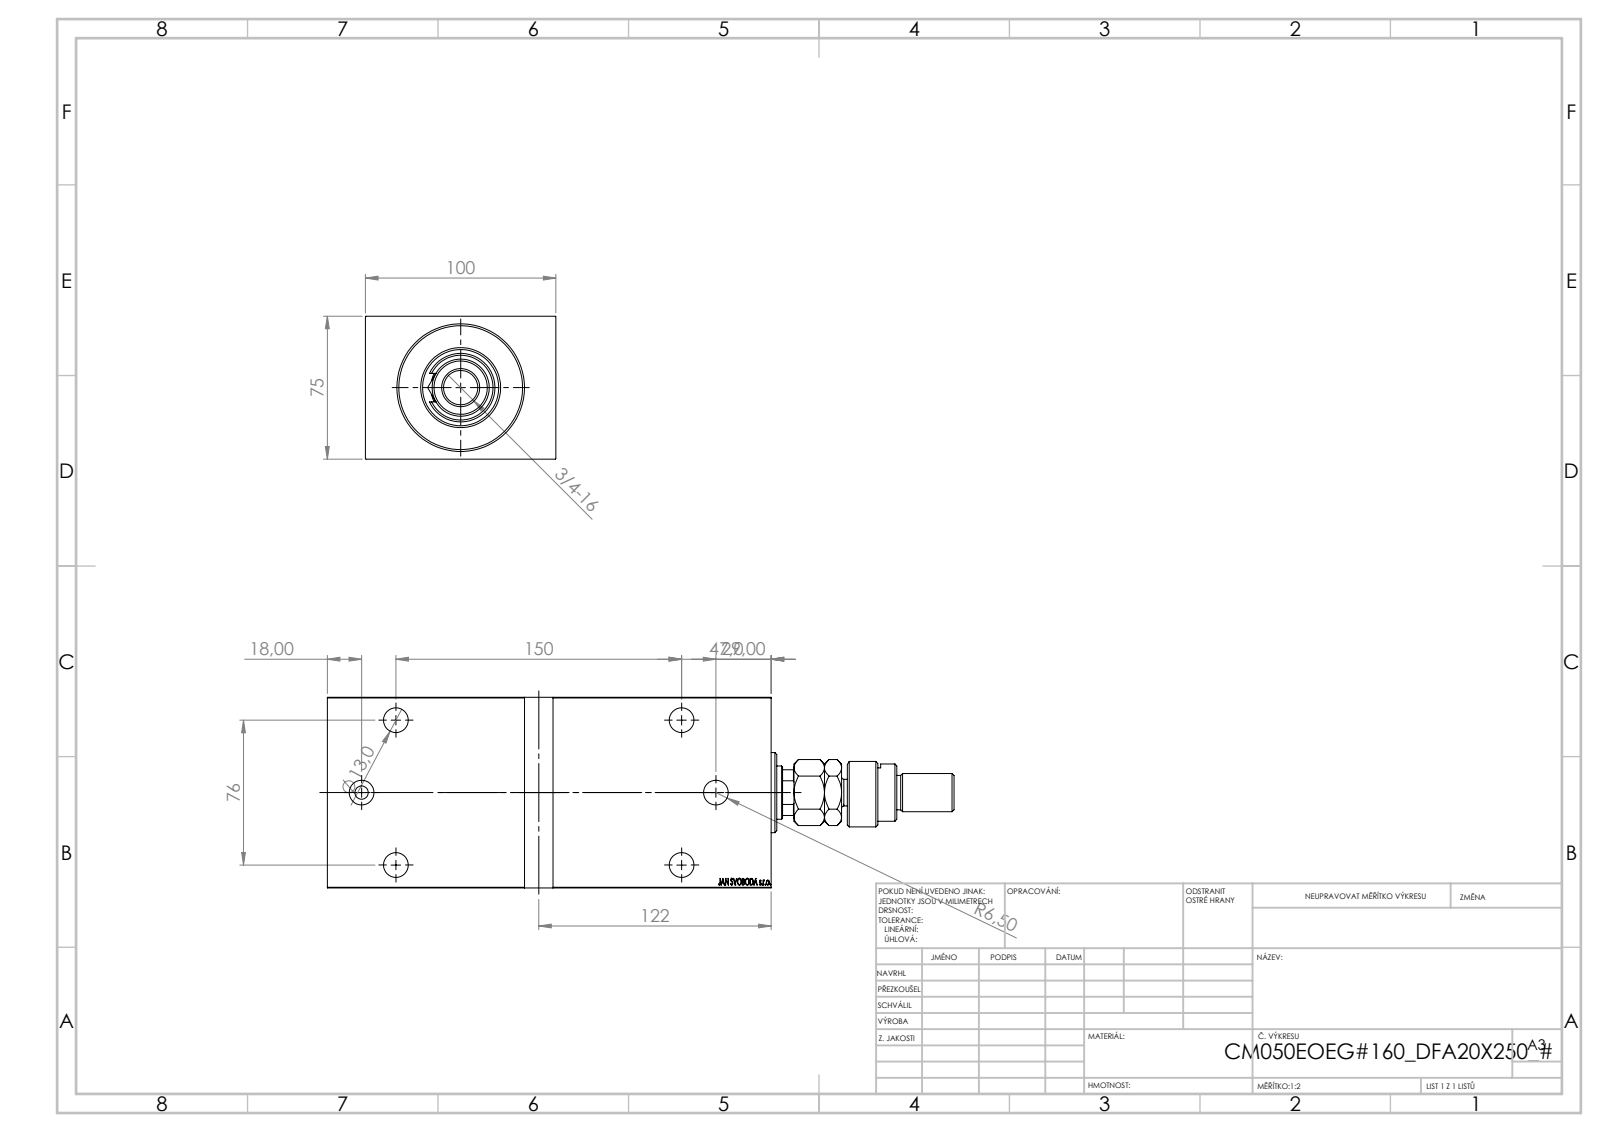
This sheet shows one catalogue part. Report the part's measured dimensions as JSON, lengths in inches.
{"part_name": "V450CM_E_VCP; V450CM_VC_B; FEMALE_PART_FOR_DFA; V450CM_E_Body (+1 more)", "step_written_by": "SolidWorks 2019 (CONFIG_CONTROL_DESIGN)", "units": "inches", "bodies": {"solids": 5, "faces": 934, "planar": 437, "cylindrical": 59, "other": 438}, "overall_size": [12.953, 3.937, 2.953], "volume_in3": 93.31, "surface_area_in2": 306, "round_holes": [[0.512, 6], [0.748, 4], [0.728, 1], [1.102, 1], [1.24, 1], [1.969, 1], [2.559, 1]], "round_bosses_or_shafts": [[2.047, 1], [1.654, 1], [1.417, 1], [1.181, 1], [0.866, 1], [0.787, 1], [0.709, 1], [0.551, 1]], "partial_cylinders_radius": [[0.295, 1], [0.472, 1], [0.531, 1]], "face_to_face_distances": [2.953, 3.937, 9.173, 8.622, 0.197, 0.551, 8.976, 8.425, 6.772, 1.181], "hole_center_spacings": [1.656, 6.781, 2.992, 5.906, 6.62, 7.323]}
